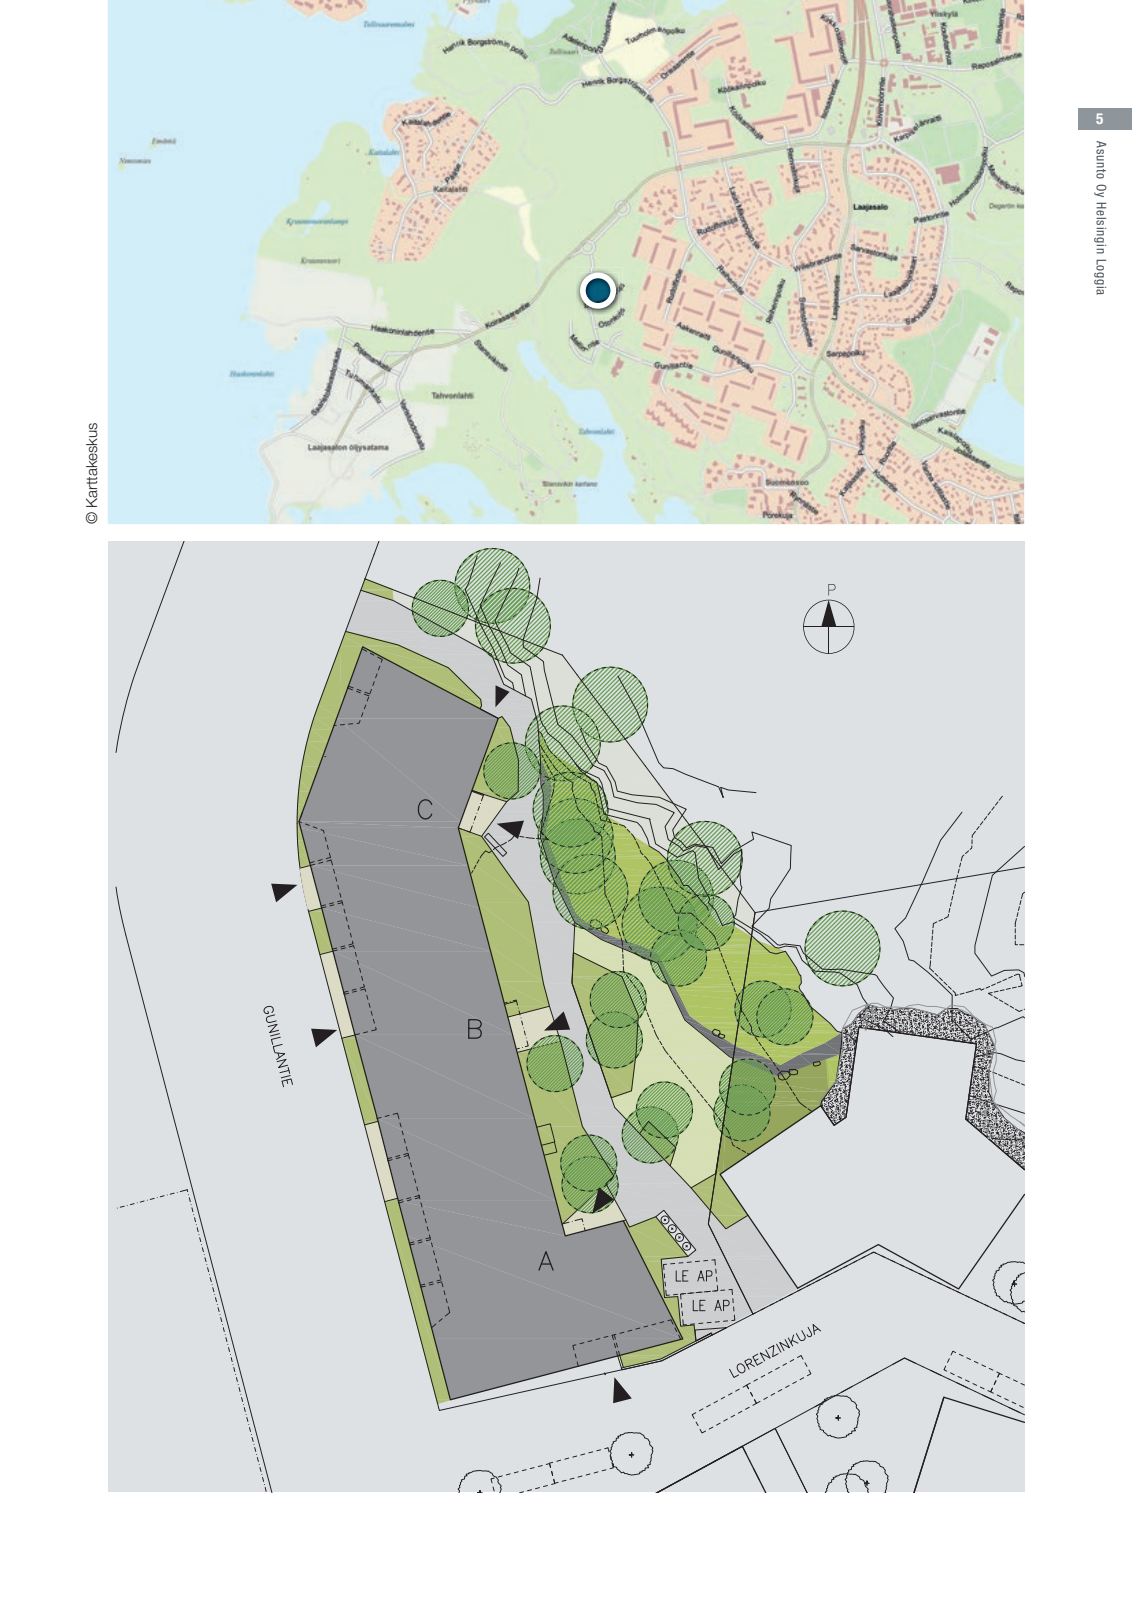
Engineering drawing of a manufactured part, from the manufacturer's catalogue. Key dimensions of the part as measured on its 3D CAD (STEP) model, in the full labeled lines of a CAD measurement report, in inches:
STEP written by: ACIS (automotive_design)
Units: inches
Bodies: 2 solids, 26 faces (8 planar, 10 cylindrical, 8 other)
Overall size (bounding box): 4.685 × 0.315 × 0.315
Volume: 0.36 in³ · Surface area: 4.862 in²
Round bosses / shafts (diameter × count): ⌀0.315 ×1
Partial cylindrical surfaces — rounded edges, fillets, slot ends (radius × count): R0.025 ×1, R0.041 ×1, R0.057 ×1, R0.154 ×1
Main face-to-face distances: 2.362, 0.016, 1.013, 1.35
